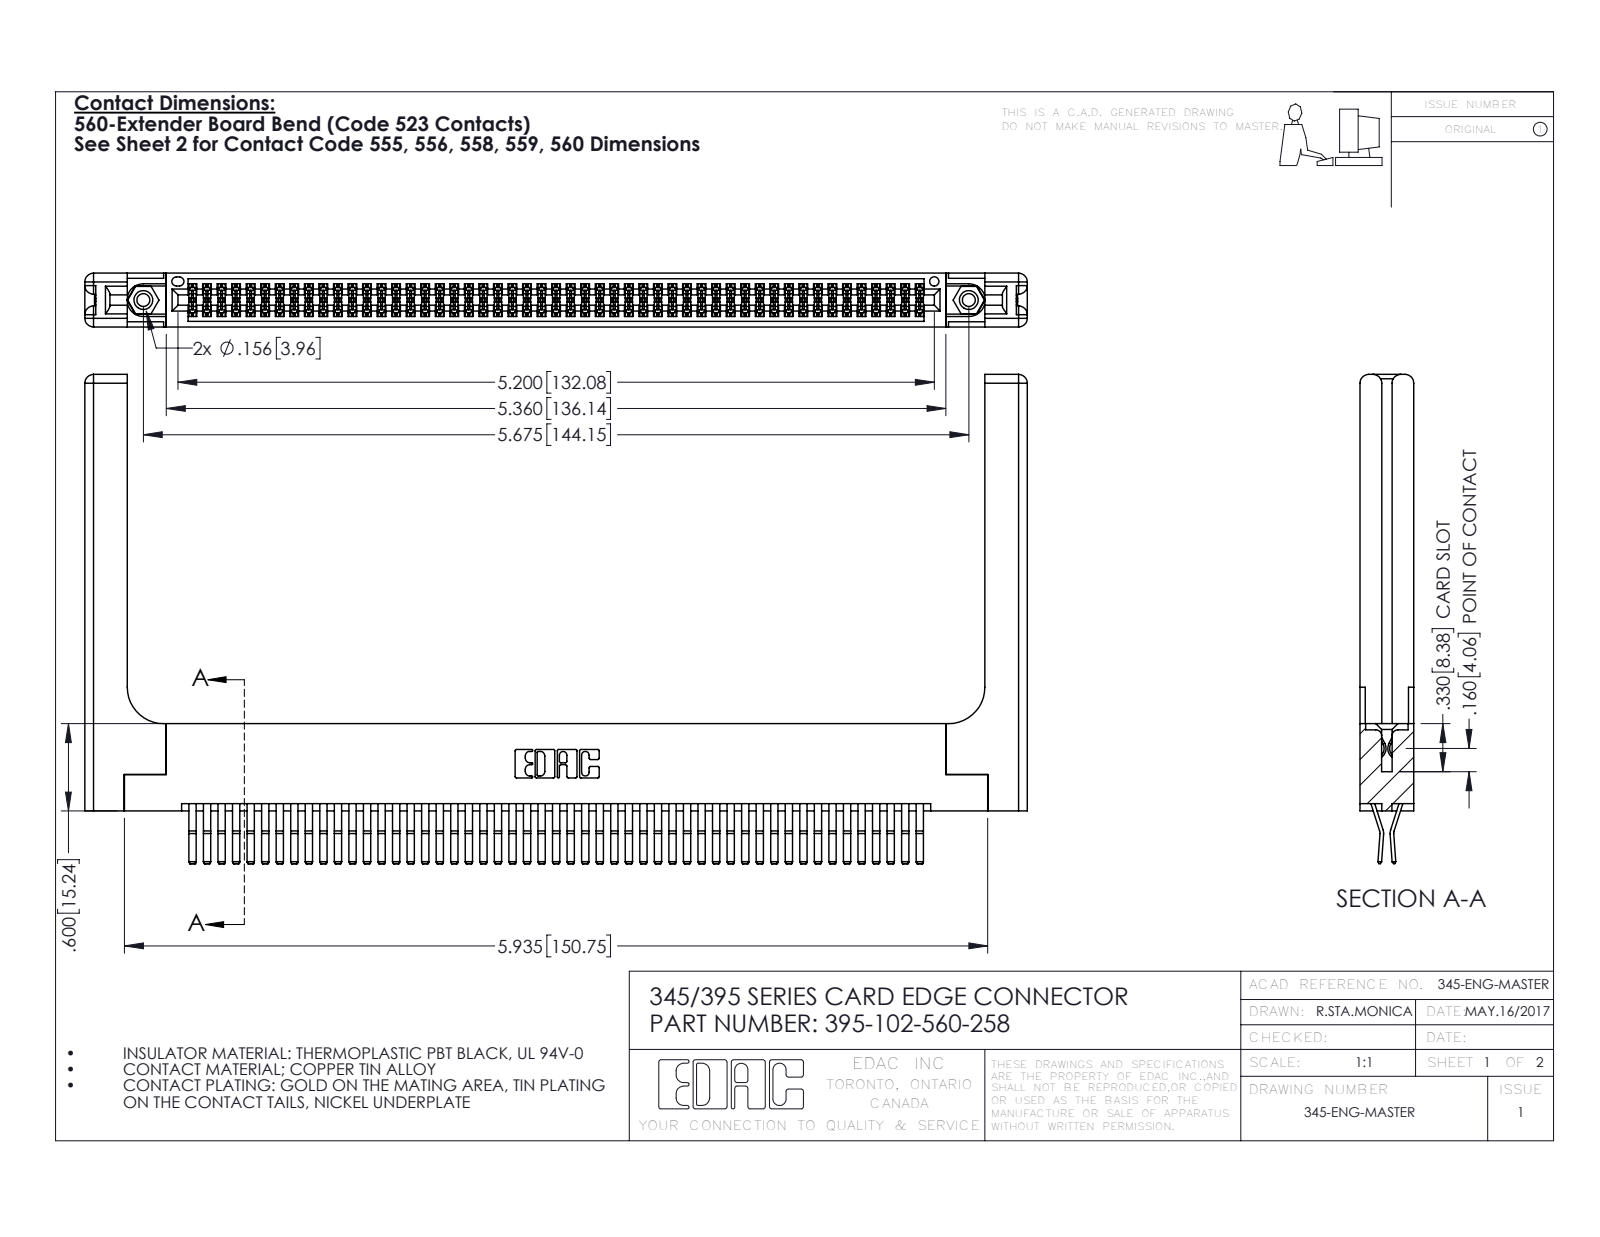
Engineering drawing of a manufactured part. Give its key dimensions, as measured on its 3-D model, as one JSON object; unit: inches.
{"part_name": "395-102-560-258; 345-292-001_560 Tail; 345-220-058_345-220-058; 345 Part_Flush Mounting Lugs - 0.156 Dia-TH (+1 more)", "step_written_by": "SolidWorks 2016 (CONFIG_CONTROL_DESIGN)", "units": "inches", "bodies": {"solids": 107, "faces": 5686, "planar": 3594, "cylindrical": 2032, "other": 60}, "overall_size": [6.479, 3.362, 0.37], "volume_in3": 1.539, "surface_area_in2": 49.13, "round_holes": [[0.089, 2], [0.125, 2], [0.156, 2], [0.064, 1]], "round_bosses_or_shafts": [[0.155, 2]], "partial_cylinders_radius": [[0.006, 154], [0.01, 22], [0.06, 16], [0.007, 6], [0.031, 6], [0.026, 3], [0.01, 2], [0.014, 2]], "face_to_face_distances": [0.072, 0.298, 0.37, 0.025, 0.2, 0.098, 0.272, 0.225, 0.148, 0.15], "hole_center_spacings": [0.27, 5.439, 5.675]}
